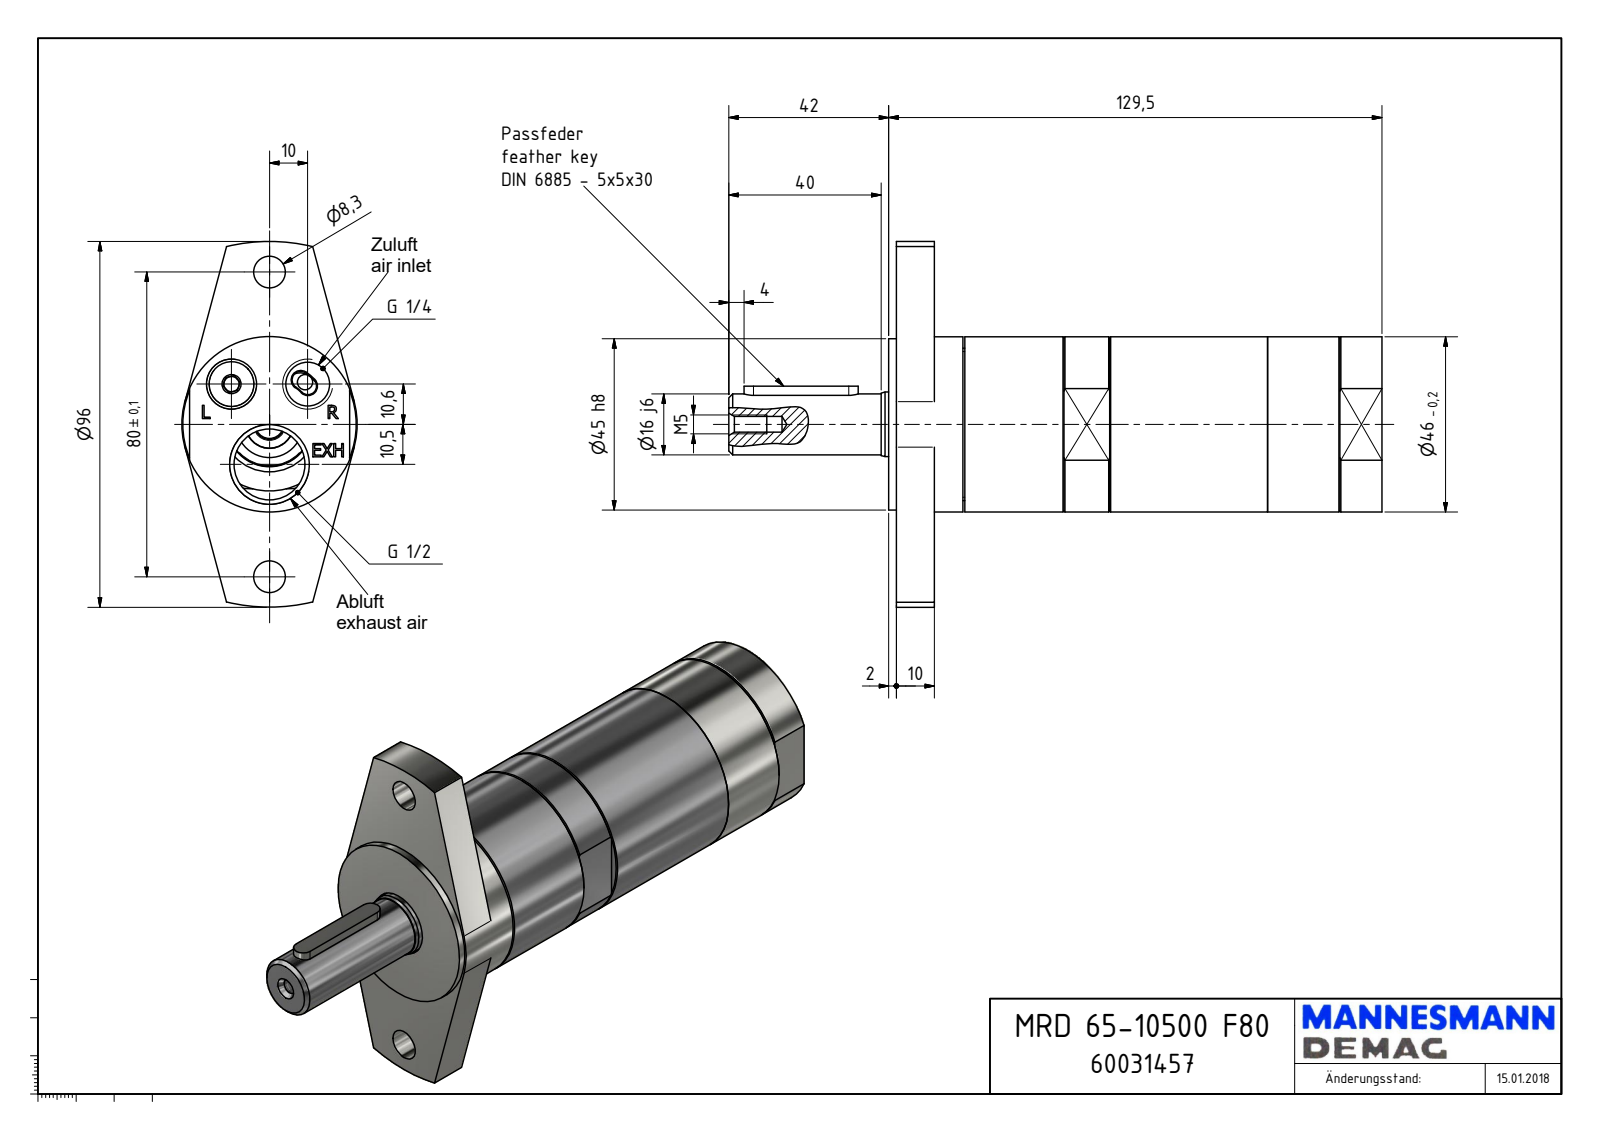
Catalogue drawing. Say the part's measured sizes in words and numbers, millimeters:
The part is named "MRD 65-10500_60031457". Its 3-D file was written by "Autodesk Inventor 2018 (AUTOMOTIVE_DESIGN)". It is 1 solid with 161 faces: 104 planar, 31 cylindrical and 26 other. Overall it measures 171.5 by 96 by 46 millimeters. Its volume is 234 478 cubic millimeters and its surface area 31 484 square millimeters. Round holes: 2 of diameter 8.3, 1 of diameter 4, 1 of diameter 4.13, 1 of diameter 11.45, 1 of diameter 17.5, 1 of diameter 18.63. Round bosses or shafts: 1 of diameter 46, 1 of diameter 45, 1 of diameter 40, 1 of diameter 16.95, 1 of diameter 16. Partial cylindrical surfaces (rounded edges, fillets, slot ends): 2 of radius 2.5, 2 of radius 5, 1 of radius 6.58, 1 of radius 9, 1 of radius 19, 1 of radius 48. The main face-to-face distances are 10, 12, 2, 129.5, 127.5, 117.5, 8, 109.5, 121.49, 119.49. The hole center spacings are 14.57, 23.35, 31.05, 40, 51.58, 10.5, 20, 29.5.
